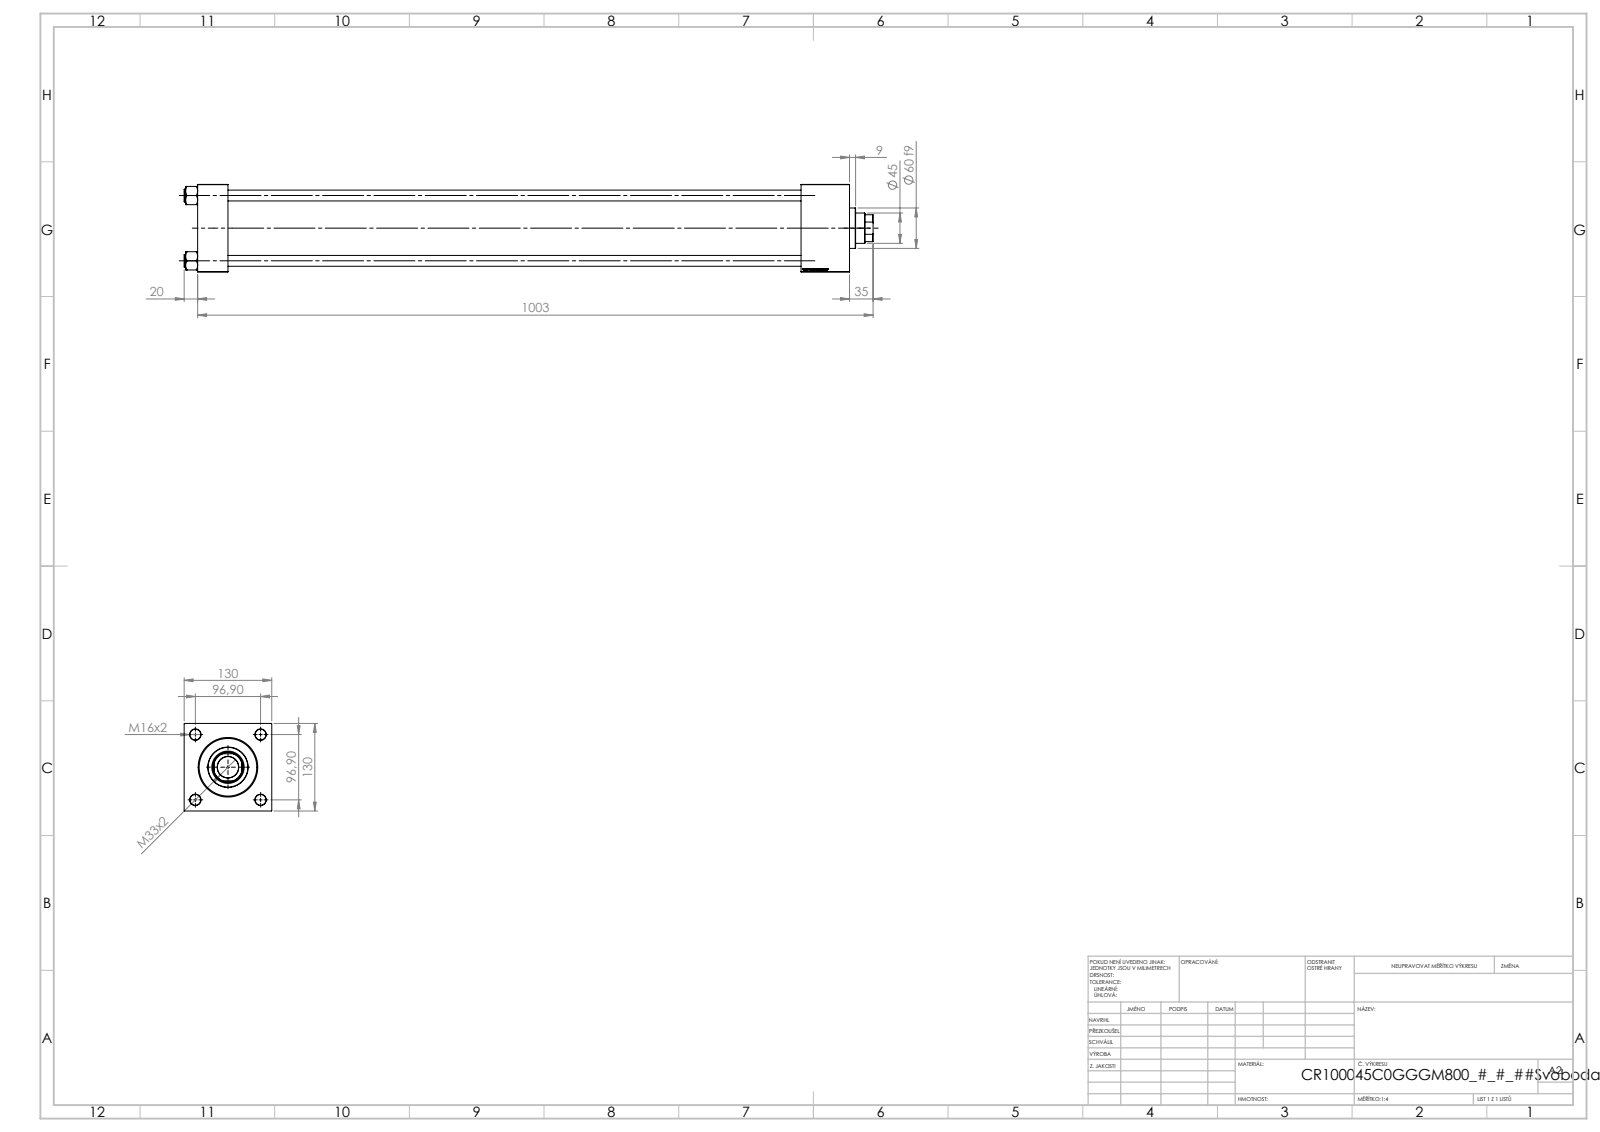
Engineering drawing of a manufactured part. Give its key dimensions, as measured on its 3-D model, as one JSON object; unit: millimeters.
{"part_name": "V215CR_C_TYCINKA; V215CR_C_Body; V215_VC_A; NUT_M5_C (+1 more)", "step_written_by": "SolidWorks 2019 (CONFIG_CONTROL_DESIGN)", "units": "millimeters", "bodies": {"solids": 11, "faces": 1197, "planar": 574, "cylindrical": 87, "other": 536}, "overall_size": [1023, 130, 130], "volume_mm3": 5050000, "surface_area_mm2": 1098000, "round_holes": [[16, 4], [7, 2], [26.44, 2], [35, 2], [31.5, 1], [45, 1], [48, 1], [76, 1], [85.5, 1], [100, 1]], "round_bosses_or_shafts": [[19, 4], [106, 1], [60, 1]], "partial_cylinders_radius": [[22, 1]], "face_to_face_distances": [130, 45, 968, 923, 896, 851, 72, 96, 51, 800], "hole_center_spacings": [68.52, 96.9, 137.04, 898.5]}
